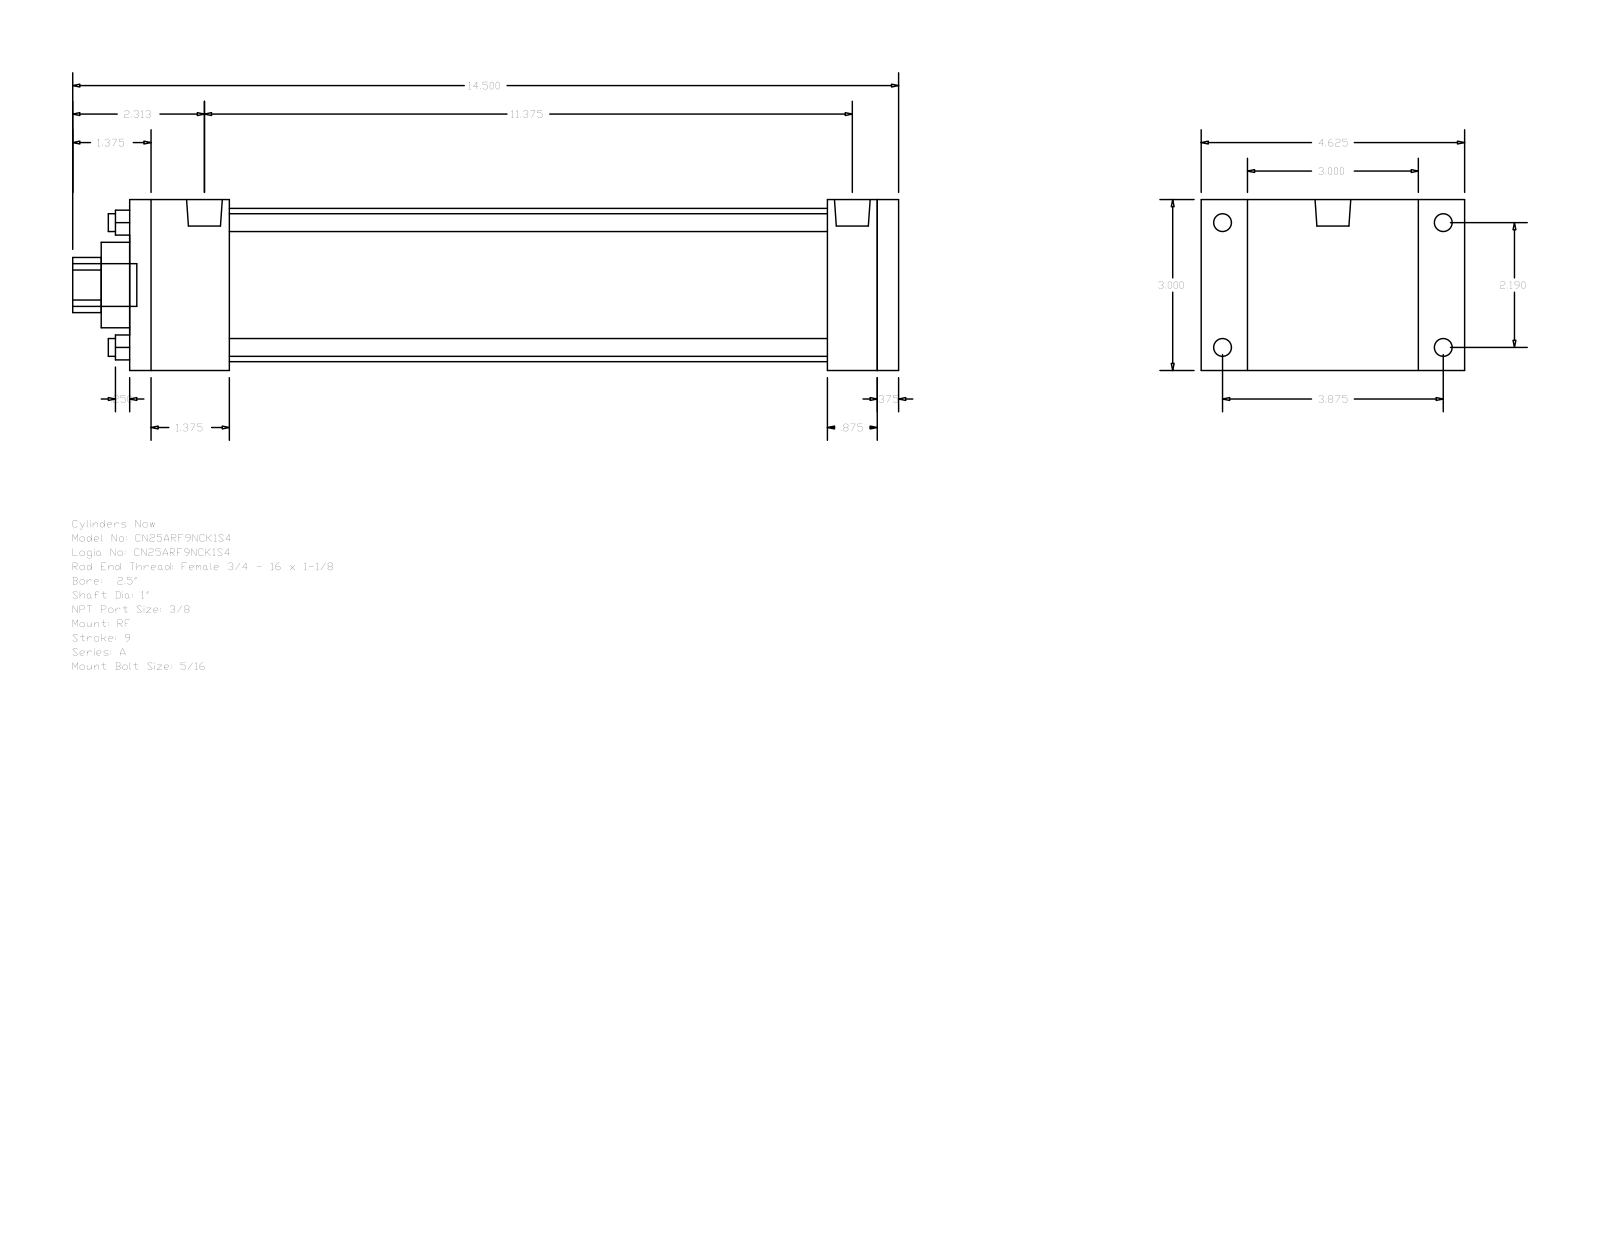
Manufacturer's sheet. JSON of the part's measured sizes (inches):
{"part_name": "A_RF__0250_1", "step_written_by": "GSSL Pune (CONFIG_CONTROL_DESIGN)", "units": "inches", "bodies": {"solids": 0, "faces": 92, "planar": 64, "cylindrical": 28, "other": 0}, "overall_size": [14.5, 4.625, 3], "round_holes": [[0.313, 4], [1, 1], [1.5, 1], [2.69, 1]], "round_bosses_or_shafts": [[0.313, 4], [0.219, 4], [0.627, 2], [0.75, 1]], "partial_cylinders_radius": [[0.484, 1]], "face_to_face_distances": [3, 13.5, 0.375, 13.125, 1.75, 12.25, 10.5, 11.375, 11.75, 0.875], "hole_center_spacings": [1.548, 2.19, 3.097]}
